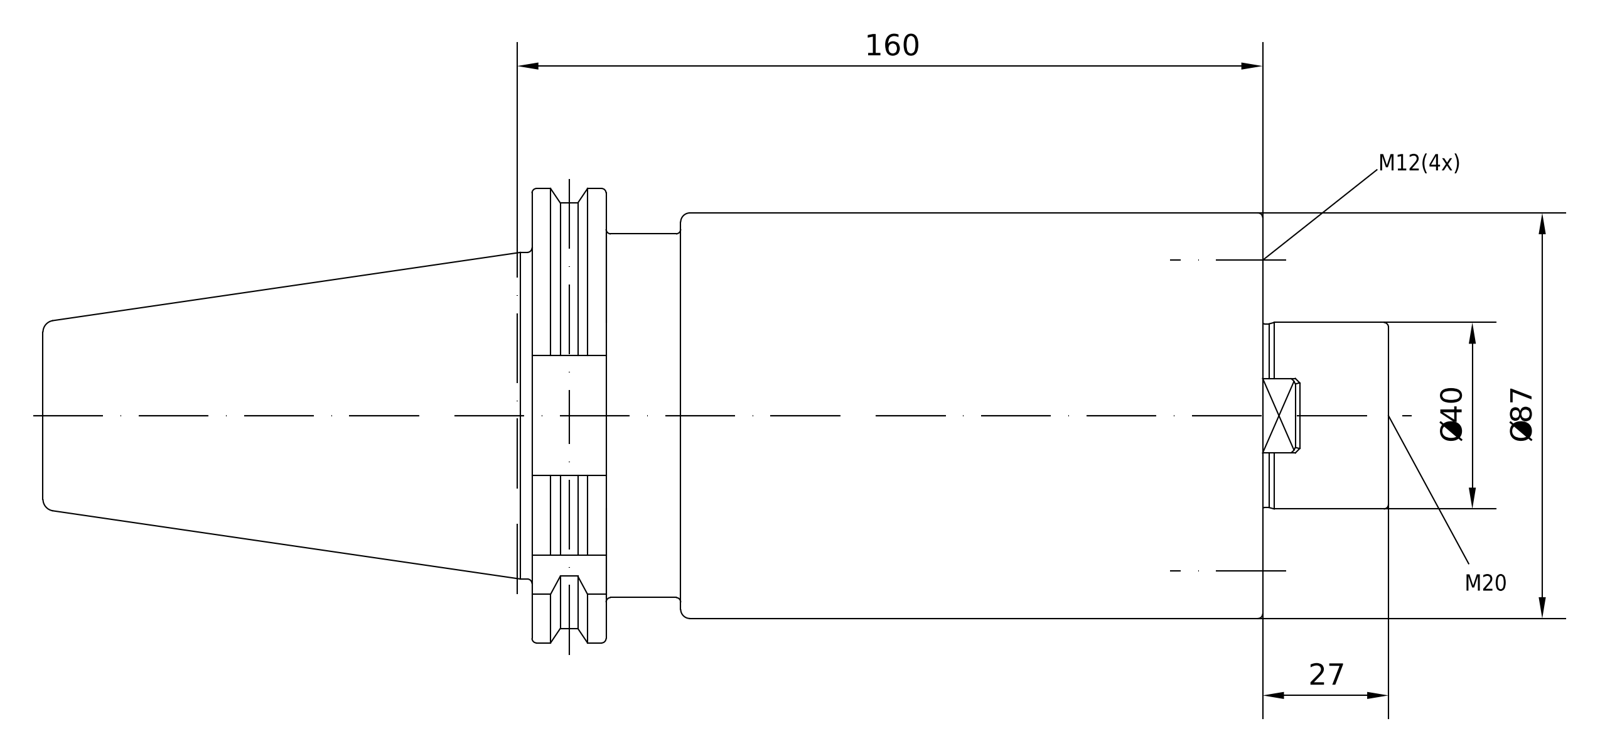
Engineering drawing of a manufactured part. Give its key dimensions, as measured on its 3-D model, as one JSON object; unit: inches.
{"part_name": "50-352-40", "step_written_by": "PRO/ENGINEER BY PARAMETRIC TECHNOLOGY CORPORATION, 2010430 (CONFIG_CONTROL_DESIGN)", "units": "inches", "bodies": {"solids": 1, "faces": 150, "planar": 40, "cylindrical": 47, "other": 63}, "overall_size": [11.362, 3.837, 3.701], "volume_in3": 73.84, "surface_area_in2": 154.7, "round_holes": [[0.402, 4], [0.472, 4], [0.689, 1], [0.787, 1], [0.817, 1], [0.985, 1], [1.012, 1]], "round_bosses_or_shafts": [[3.583, 1], [3.504, 1], [2.722, 1], [1.575, 1], [0.945, 1]], "partial_cylinders_radius": [[0.069, 1], [1.535, 1], [1.919, 1]], "face_to_face_distances": [6.173, 0.624, 5.549, 0.63, 1.254, 4.919, 7.236, 6.612, 5.982, 1.063], "hole_center_spacings": [1.313, 1.857, 2.626]}
